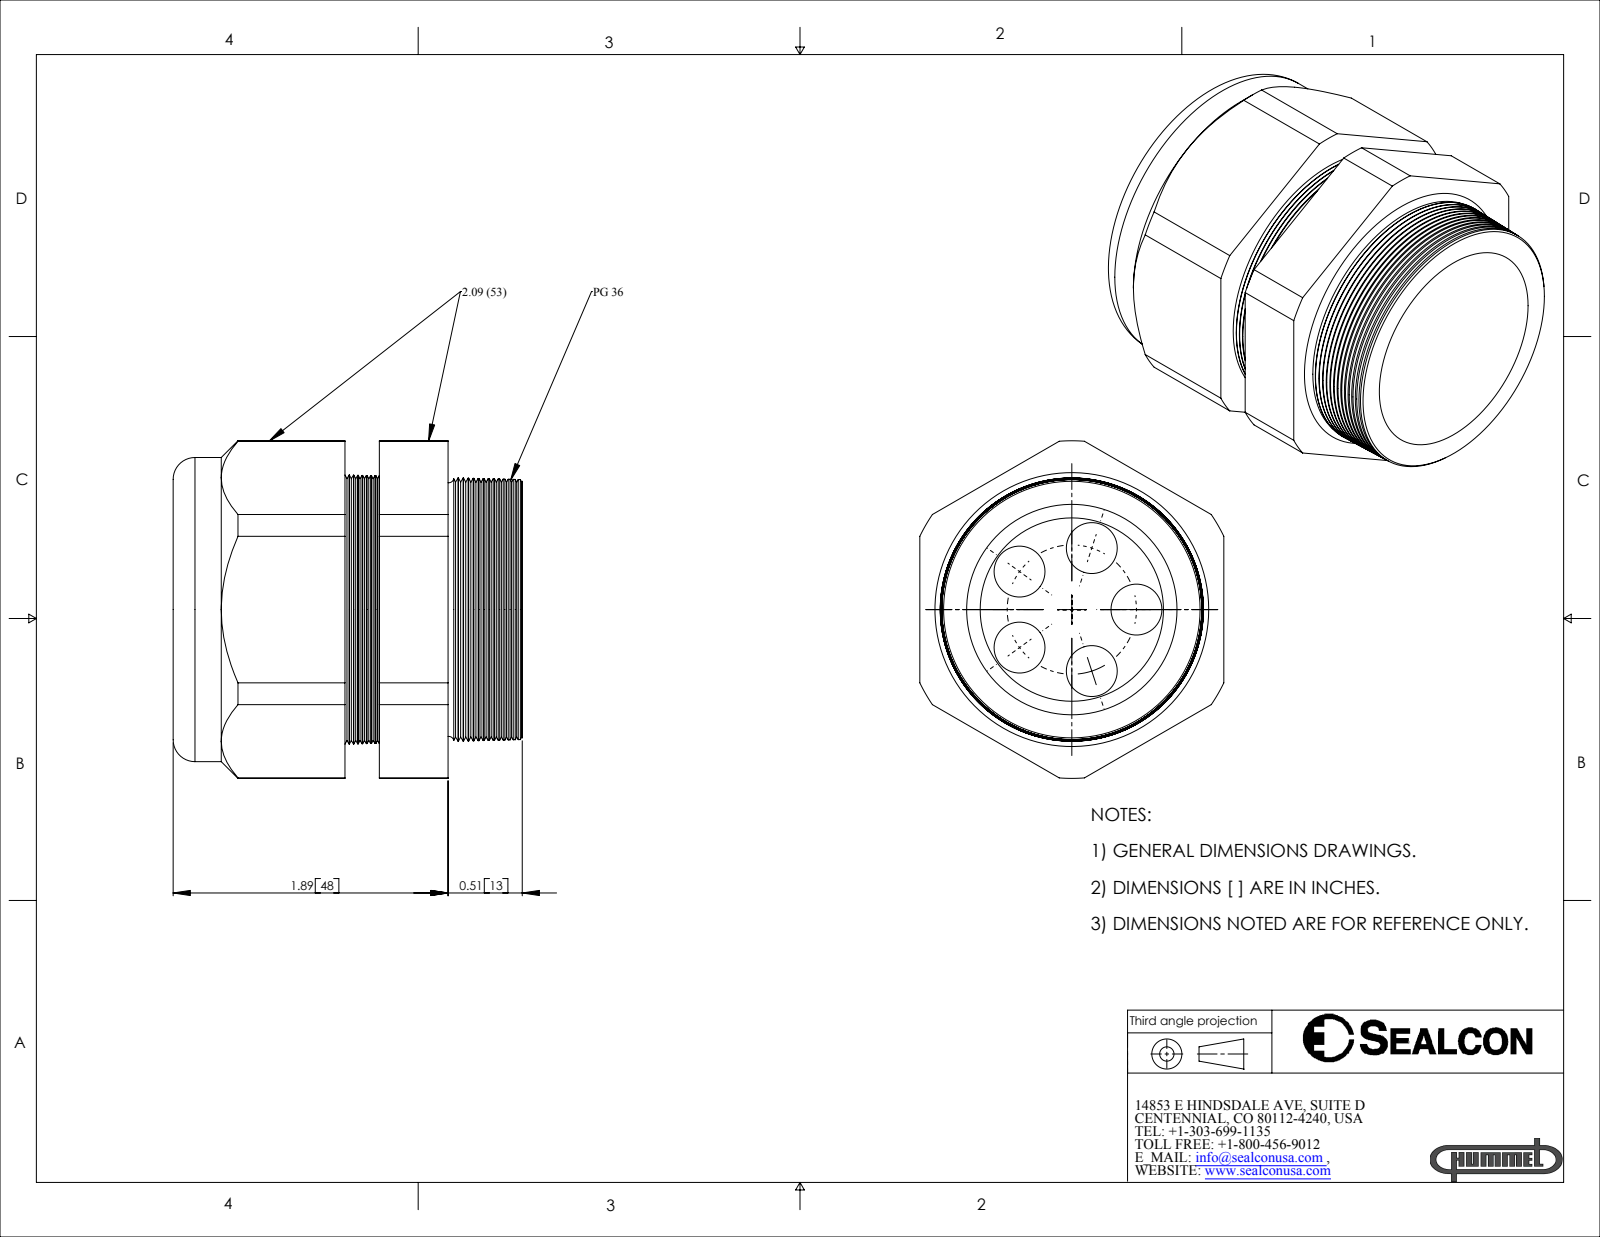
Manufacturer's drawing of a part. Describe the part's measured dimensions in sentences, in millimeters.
The part is named "CD36A1-BK". Its 3-D file was written by "SolidWorks 2007 (CONFIG_CONTROL_DESIGN)". It is 2 solids with 199 faces: 21 planar, 30 cylindrical and 148 other. Overall it measures 61 by 58.9 by 53.1 millimeters. Its volume is 83 210 cubic millimeters and its surface area 26 790 square millimeters. Round holes: 5 of diameter 8.9, 1 of diameter 31.5, 1 of diameter 32. Round bosses or shafts: 1 of diameter 53.1. Partial cylindrical surfaces (rounded edges, fillets, slot ends): 1 of radius 29.5. The main face-to-face distances are 53.1, 36, 30, 6, 48, 18, 12, 61, 31, 24.9. The hole center spacings are 11.3, 13.3, 21.5, 21.5, 11.3, 13.3.
